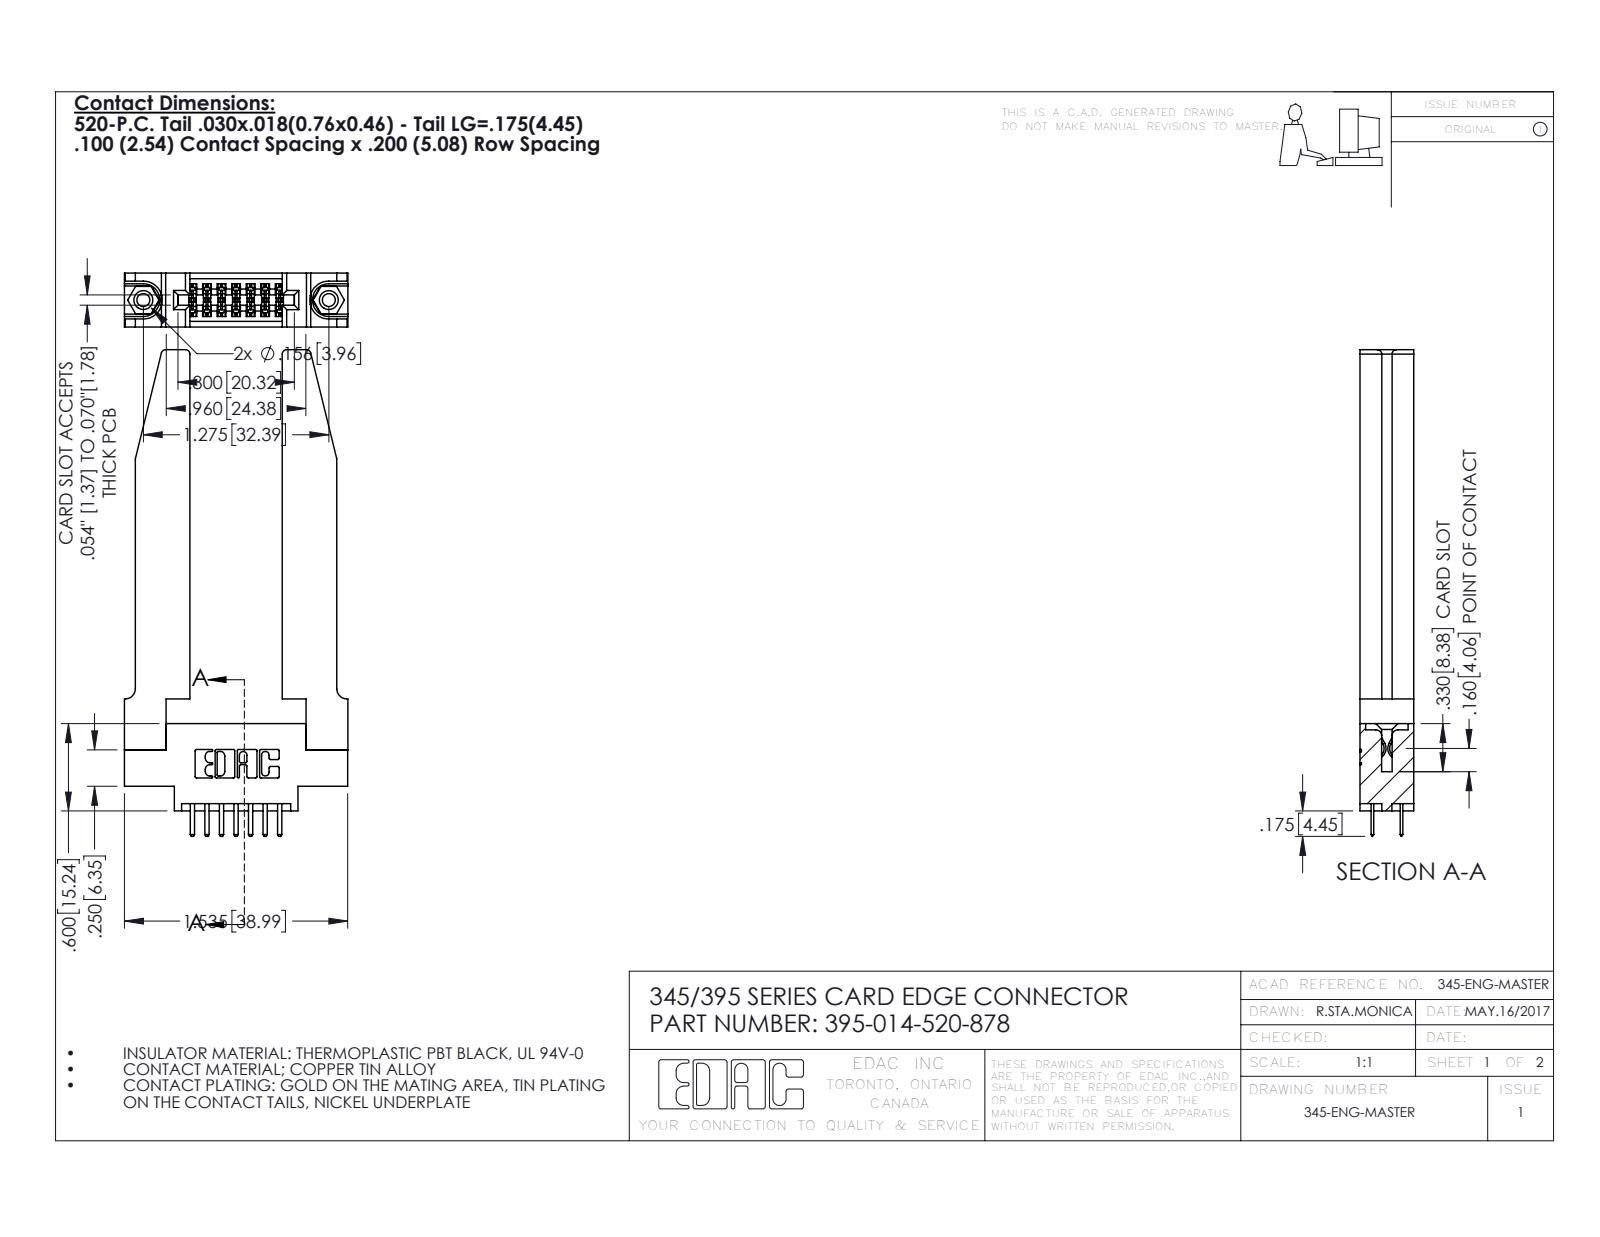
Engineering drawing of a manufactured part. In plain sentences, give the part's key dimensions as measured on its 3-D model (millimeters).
The part is named "345-250-001_345-250-001-102; 345-220-078_345-220-078; 345-292-001_345-293-120; 395-014-520-878 (+1 more)". Its 3-D file was written by "SolidWorks 2016 (CONFIG_CONTROL_DESIGN)". It is 19 solids with 1120 faces: 716 planar, 352 cylindrical and 52 other. Overall it measures 85 by 39 by 9.4 millimeters. Its volume is 11 100 cubic millimeters and its surface area 11 240 square millimeters. Round holes: 2 of diameter 2.3, 2 of diameter 3.2, 2 of diameter 4, 1 of diameter 1.6. Round bosses or shafts: 2 of diameter 3.9. Partial cylindrical surfaces (rounded edges, fillets, slot ends): 22 of radius 0.3, 21 of radius 0.2, 18 of radius 0.3, 8 of radius 0.8, 6 of radius 0.2, 6 of radius 0.8, 3 of radius 0.7, 2 of radius 0.4. The main face-to-face distances are 9.4, 3.8, 5.6, 1.8, 7.6, 2, 3.8, 16.1, 2.4, 5.1. The hole center spacings are 6.9, 26.5, 32.4.
